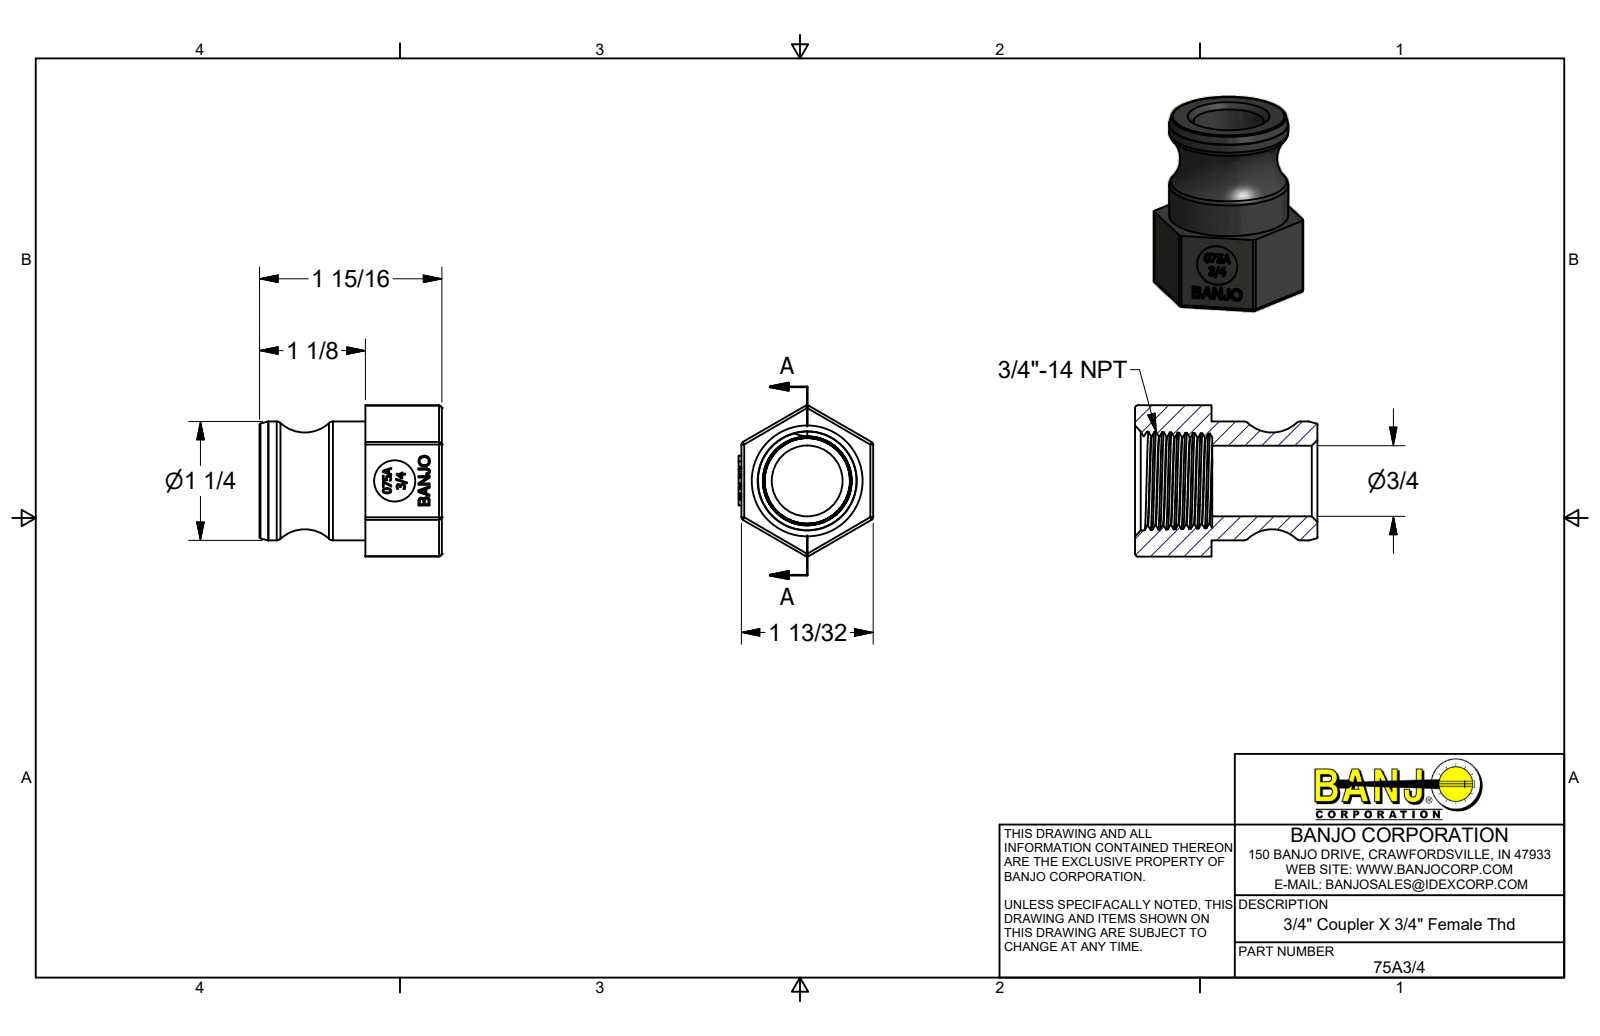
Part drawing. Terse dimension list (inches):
name: 75A075; 75A075U
written by: Autodesk Inventor 2017 (AUTOMOTIVE_DESIGN)
unit: in
bodies: 1 solid, 228 faces (117 planar, 17 cylindrical, 94 other)
size: 1.937 × 1.607 × 1.43
volume: 1.483 in³; area: 17.28 in²
holes: 1× ⌀0.437, 1× ⌀0.75
bosses: 1× ⌀1.264
rounds: 6× R0.03, 6× R0.031, 1× R0.313
face distances: 1.4, 1.937, 1.125, 0.813, 1.117, 0.82, 1.39, 1.43, 0.04, 0.03
